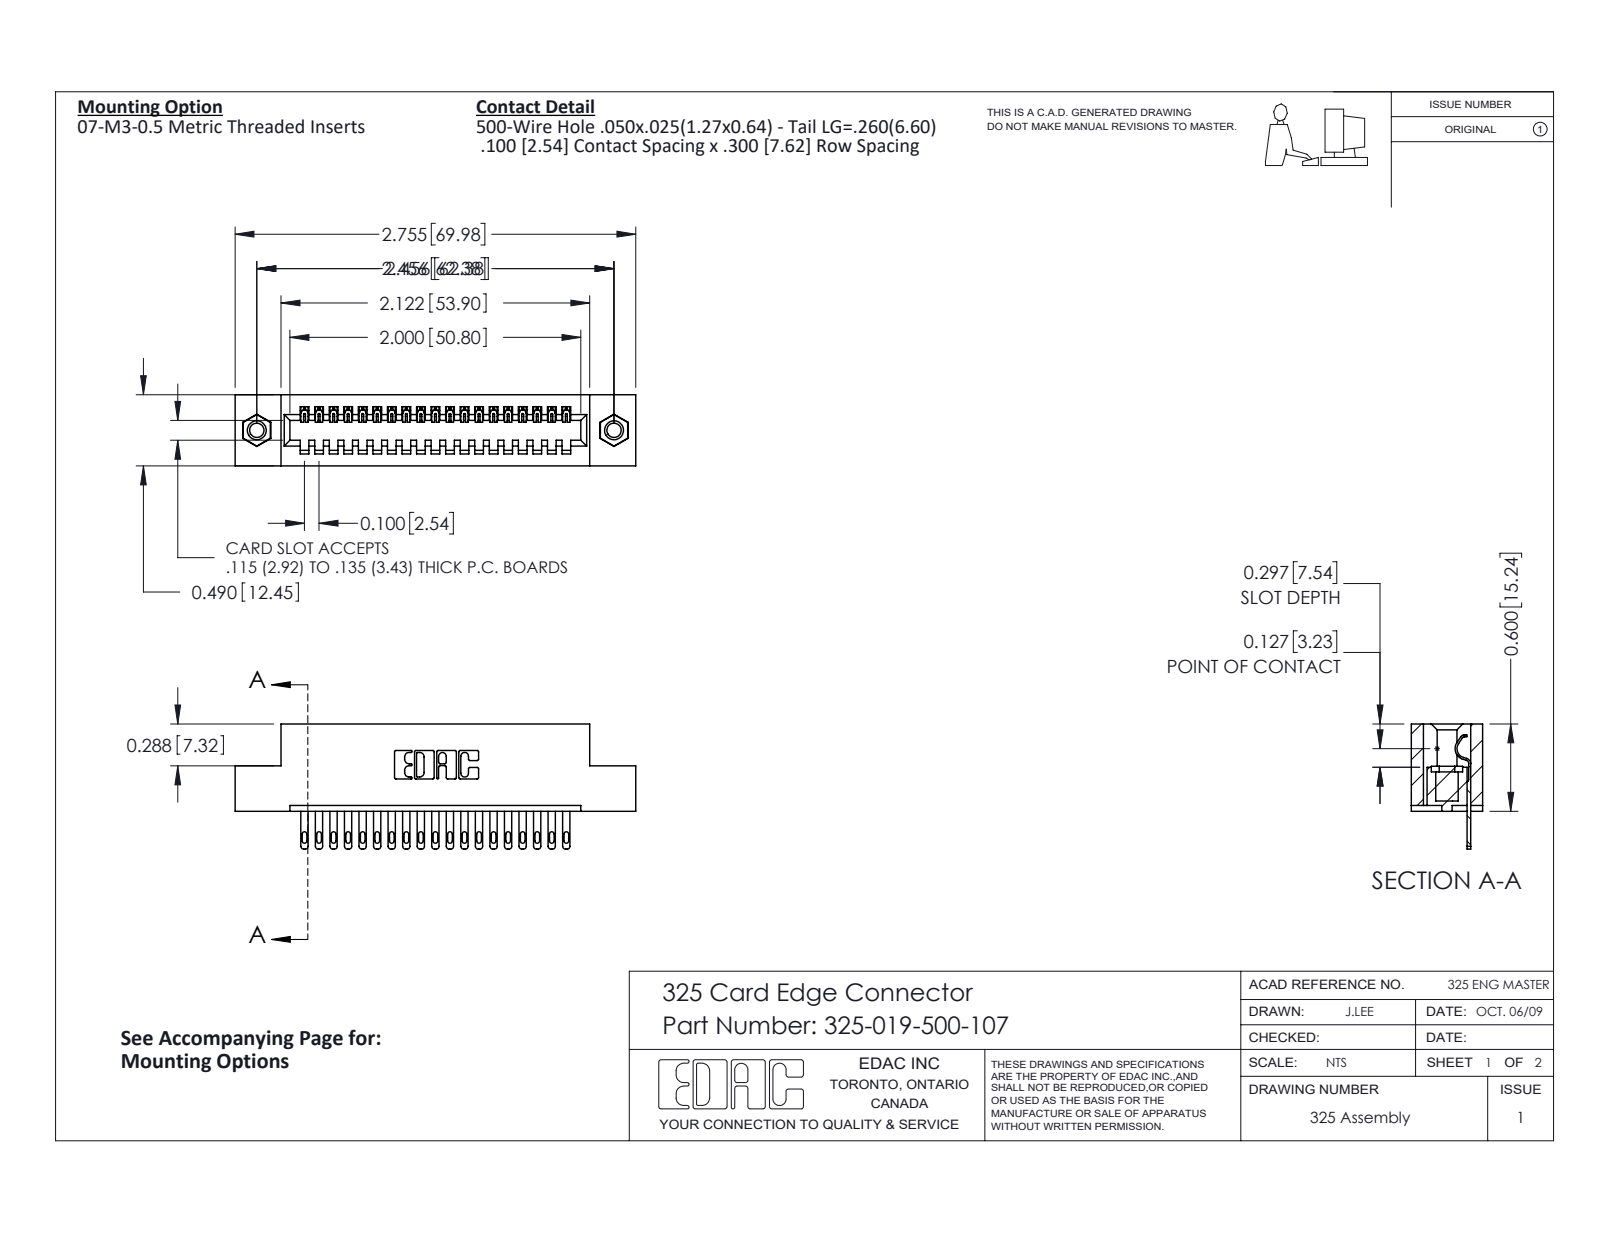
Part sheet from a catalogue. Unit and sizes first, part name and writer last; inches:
Units: inches
Overall size (bounding box): 2.755 × 0.86 × 0.49
Round holes (diameter × count): ⌀0.098 ×2, ⌀0.125 ×2, ⌀0.16 ×2
Round bosses / shafts (diameter × count): ⌀0.155 ×2
Partial cylindrical surfaces — rounded edges, fillets, slot ends (radius × count): R0.006 ×38, R0.016 ×38, R0.02 ×38, R0.01 ×22, R0.007 ×6, R0.031 ×6, R0.026 ×3, R0.014 ×1
Main face-to-face distances: 0.083, 0.407, 0.3, 0.49, 0.107, 0.383, 0.025, 0.04, 0.1, 0.6
Hole centre spacings: 2.456
Volume: 0.531 in³ · Surface area: 14.24 in²
Bodies: 22 solids, 1200 faces (786 planar, 398 cylindrical, 16 other)
Part name (STEP PRODUCT): 325 Part_TI; 345-250-001_345-250-005-103; 325-292-001_325-293-100; 325-019-500-107
STEP written by: SolidWorks 2016 (CONFIG_CONTROL_DESIGN)
